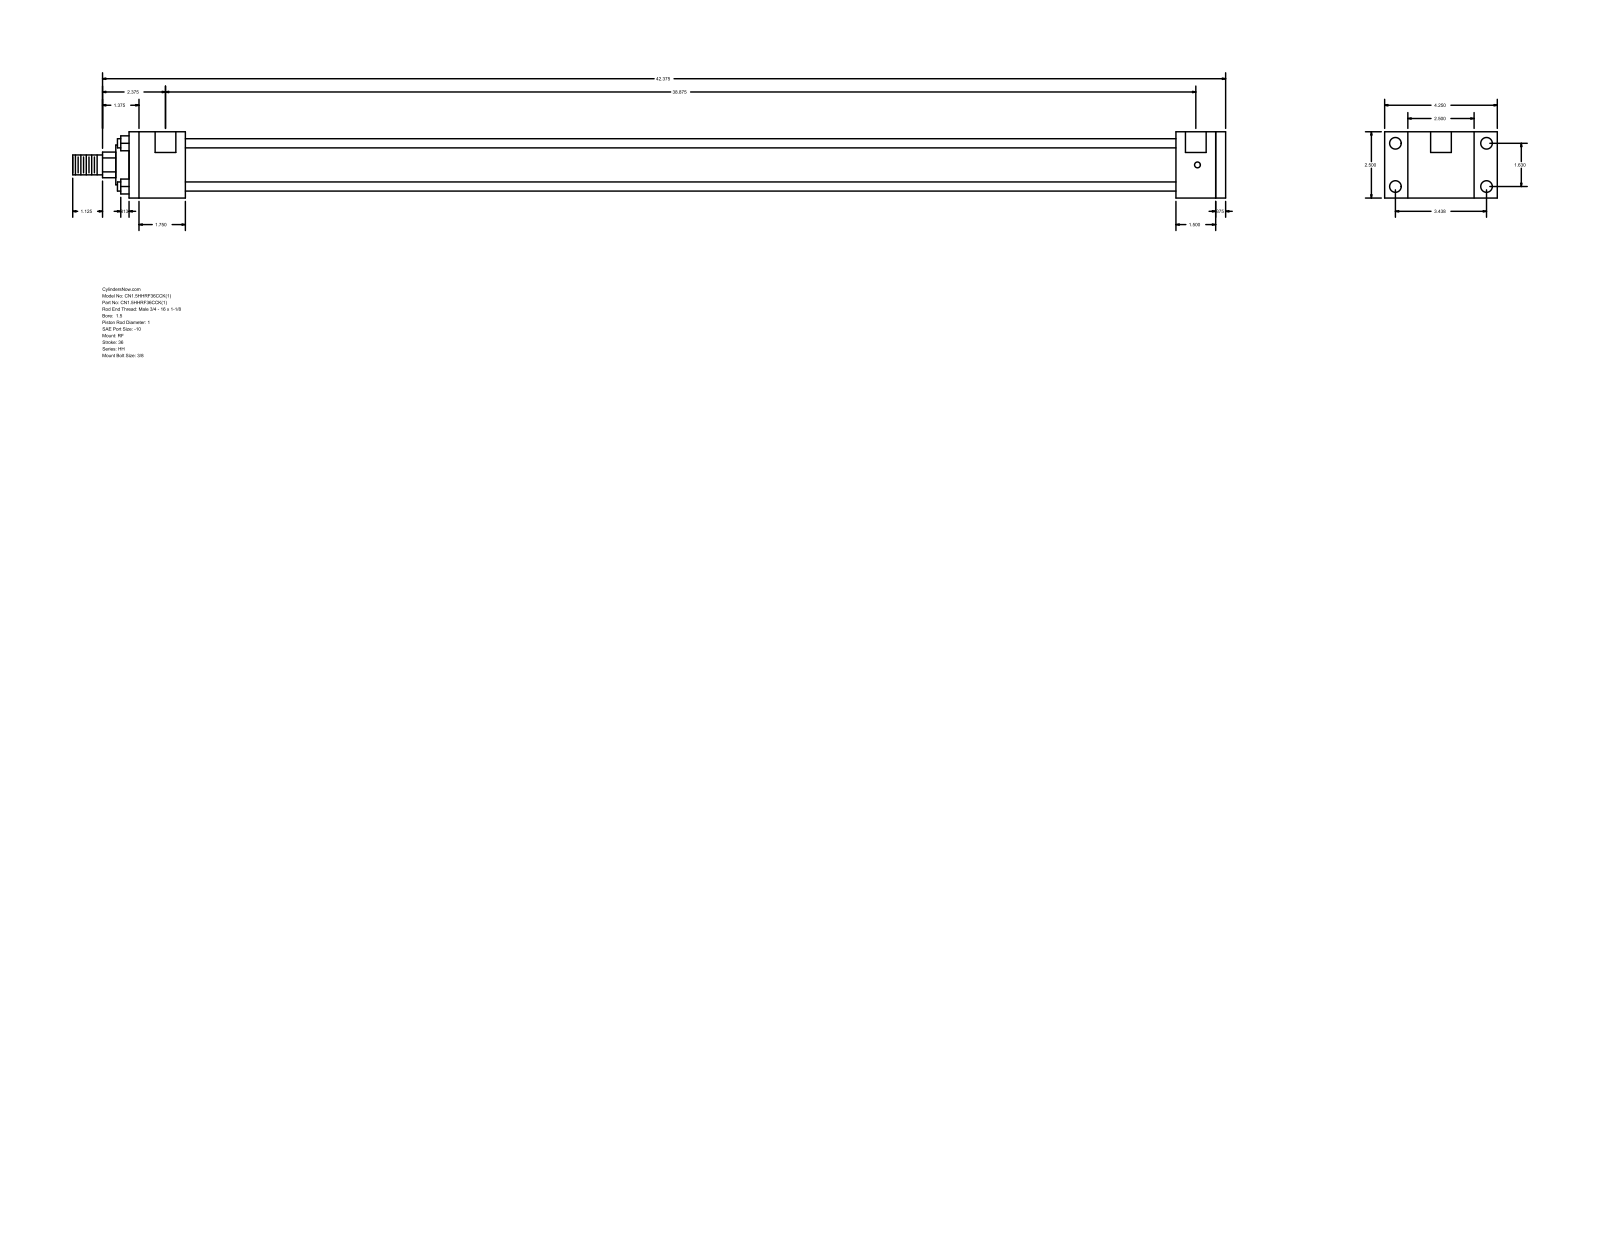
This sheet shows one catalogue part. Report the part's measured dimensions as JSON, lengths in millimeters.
{"part_name": "HH_RF__0150_1", "step_written_by": "GSSL Pune (CONFIG_CONTROL_DESIGN)", "units": "millimeters", "bodies": {"solids": 0, "faces": 92, "planar": 64, "cylindrical": 28, "other": 0}, "overall_size": [1104.9, 107.95, 63.5], "round_holes": [[5.56, 4], [11.13, 4], [19.84, 2]], "round_bosses_or_shafts": [[8.76, 4], [44.45, 1], [38.1, 1], [25.4, 1], [19.05, 1]], "partial_cylinders_radius": [[12.29, 1]], "face_to_face_distances": [63.5, 9.53, 38.1, 949.32, 987.42, 996.95, 47.63, 53.98, 1003.3, 1041.4], "hole_center_spacings": [1.59, 41.4, 87.32, 96.64, 989.01, 990.6, 987.42]}
